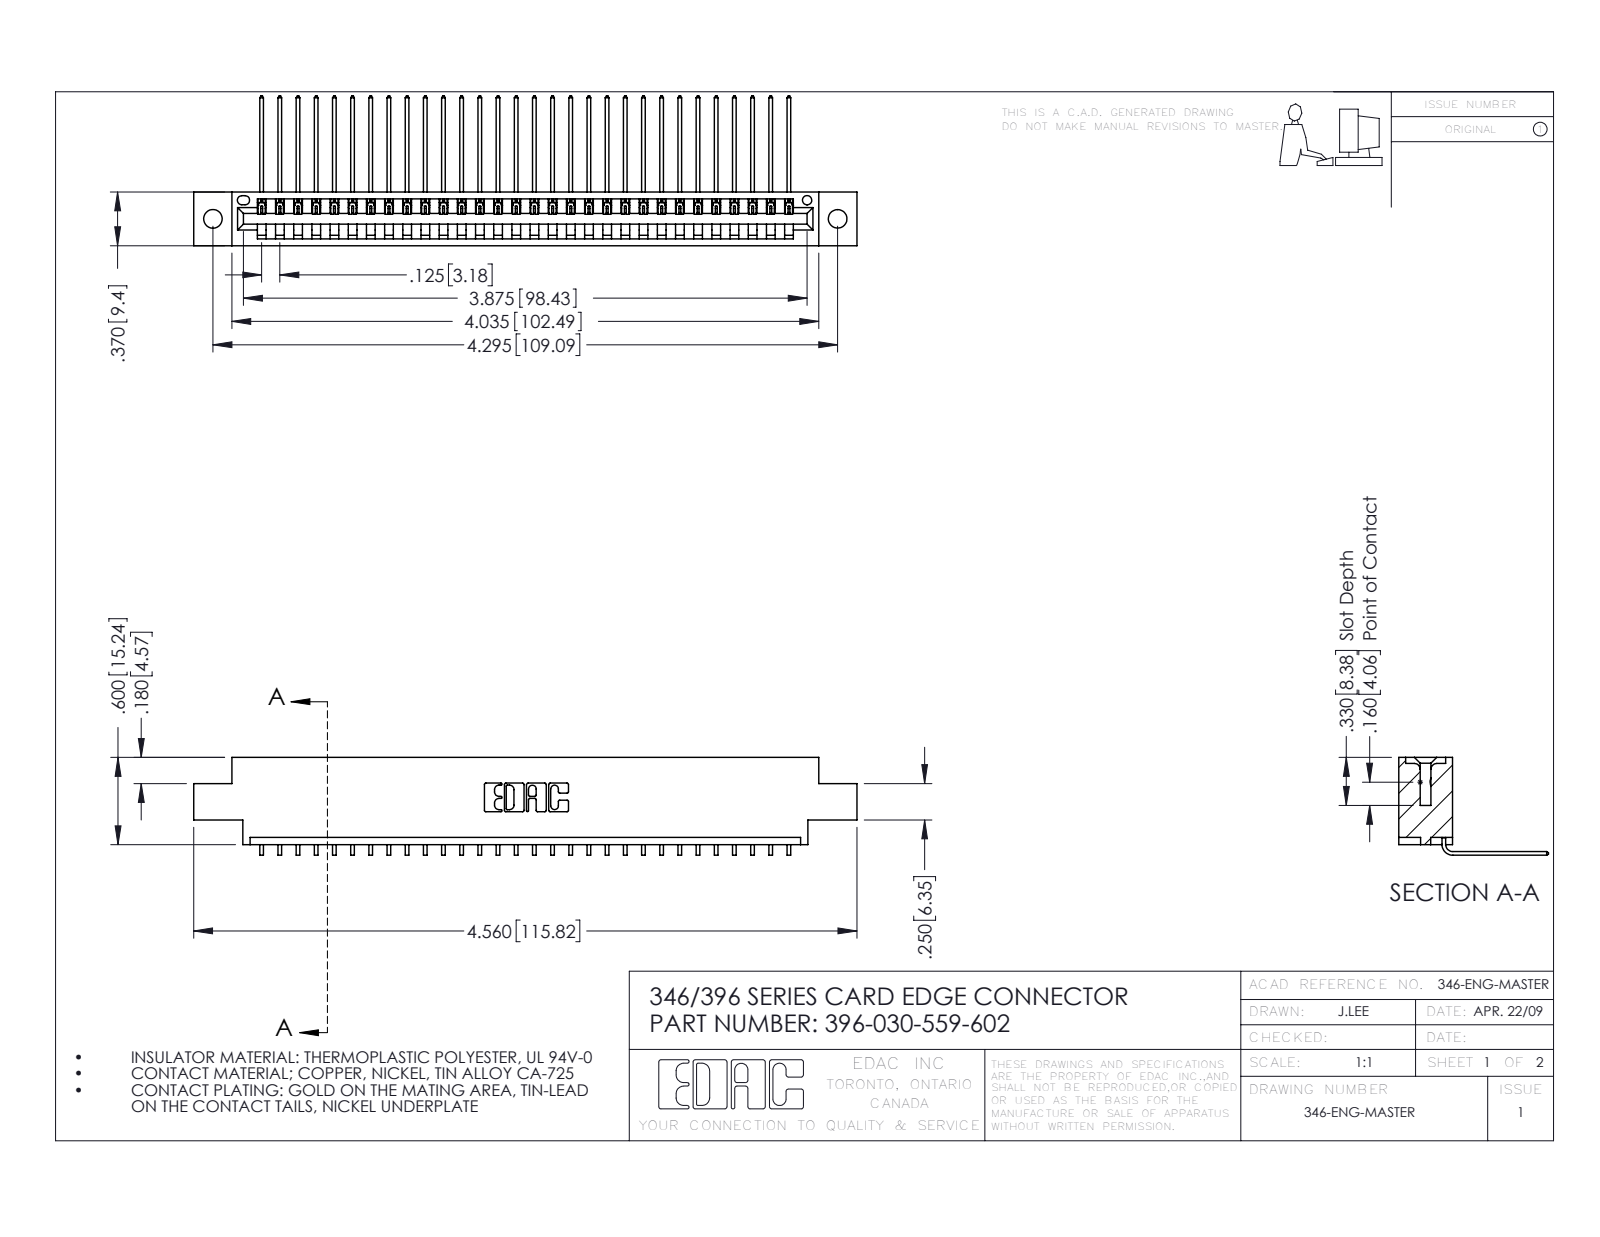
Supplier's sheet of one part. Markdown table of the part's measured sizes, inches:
| quantity | value |
| --- | --- |
| part name | 396-030-559-602; 346 Part_0.170 Offset - 0.128 Dia; 345-292-001_558 559 Tail - 1 |
| STEP written by | SolidWorks 2016 (CONFIG_CONTROL_DESIGN) |
| units | inches |
| bodies | 31 solids, 1926 faces (1340 planar, 586 cylindrical, 0 other) |
| overall size | 4.56 × 1.03 × 0.673 |
| volume | 0.666 in³ |
| surface area | 21.69 in² |
| round holes (diameter × count) | 0.128 × 2, 0.064 × 1 |
| partial cylindrical surfaces (radius × count) | 0.006 × 60, 0.01 × 22, 0.007 × 6, 0.031 × 6, 0.026 × 3, 0.031 × 2, 0.04 × 2, 0.014 × 1 |
| main face-to-face distances | 0.048, 0.322, 0.37, 0.25, 0.025, 0.072, 0.148, 0.222, 0.1, 0.174 |
| hole center spacings | 0.246, 4.087, 4.295 |
